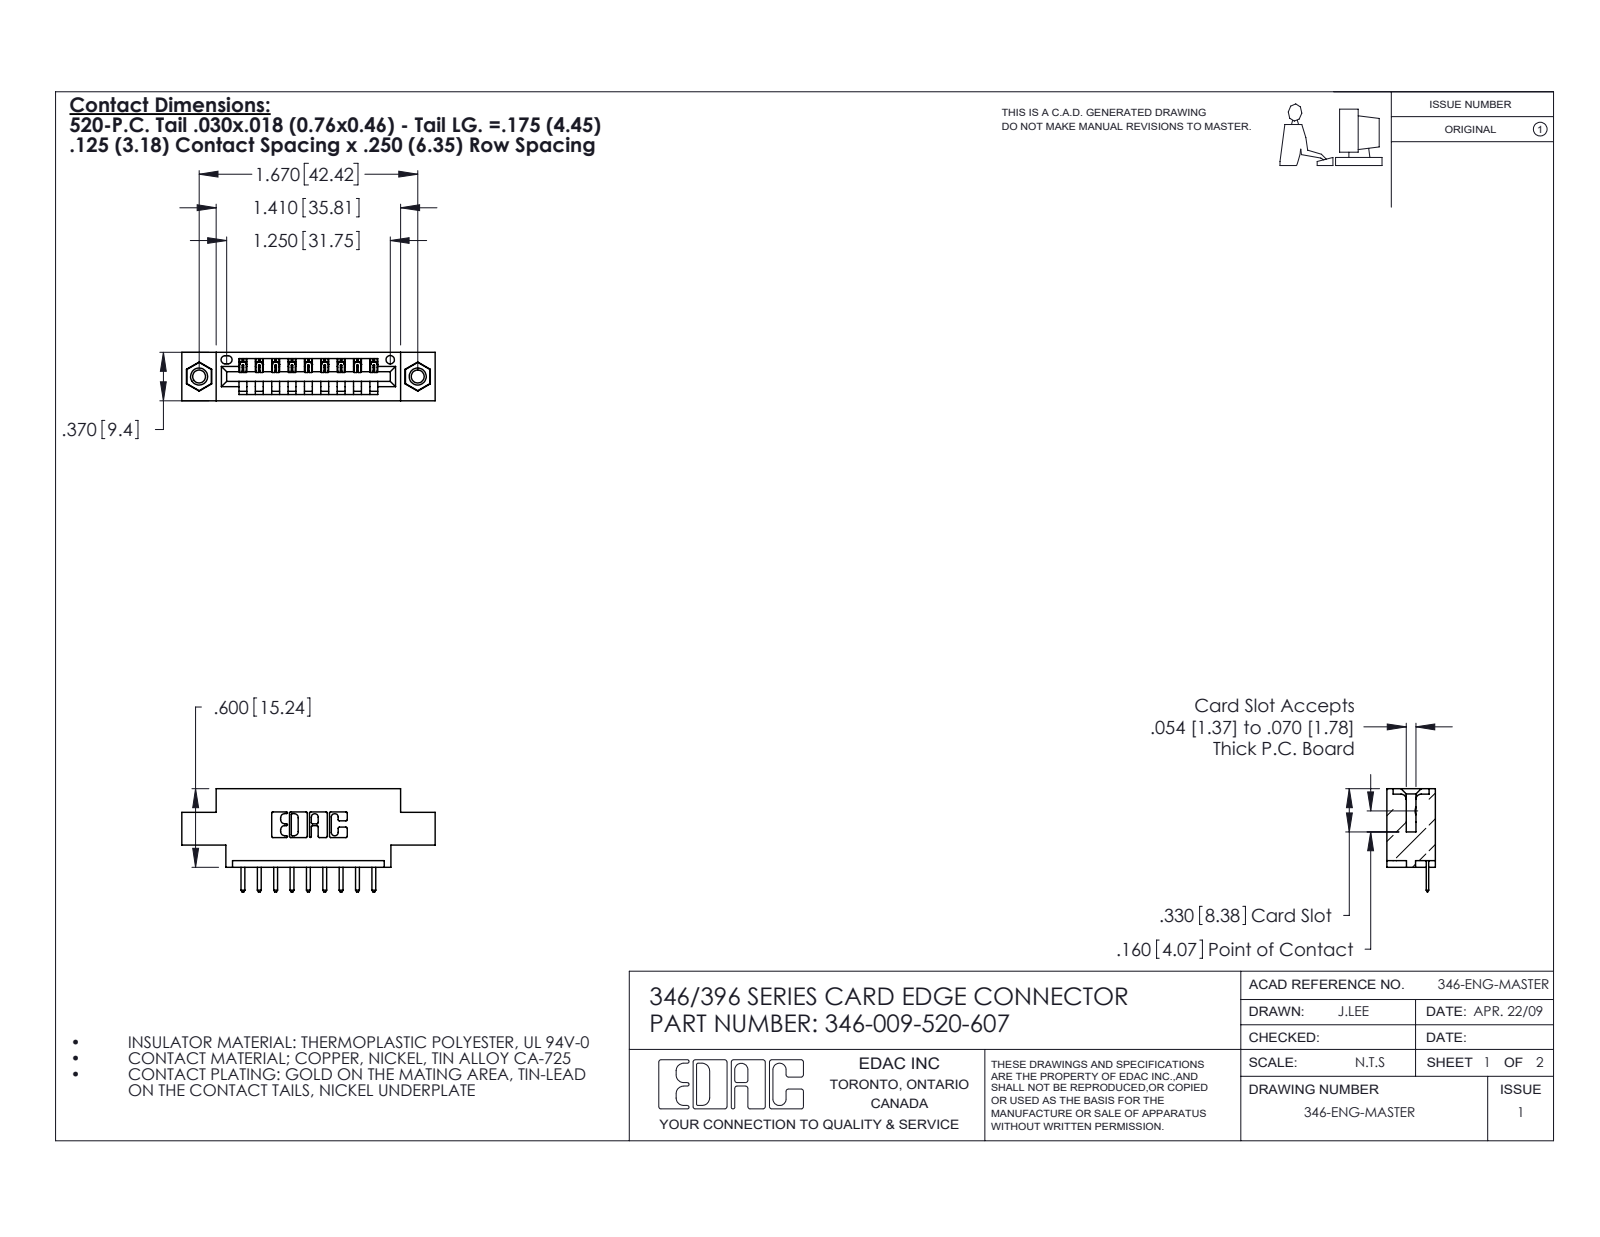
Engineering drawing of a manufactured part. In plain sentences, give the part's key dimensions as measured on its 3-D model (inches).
The part is named "346-009-520-607; 345-250-001_345-250-005-103; 345-292-001_345-293-120; 346 Part_0.170 Offset - 0.156 Dia-TI". Its 3-D file was written by "SolidWorks 2020 (CONFIG_CONTROL_DESIGN)". It is 12 solids with 744 faces: 490 planar, 238 cylindrical and 16 other. Overall it measures 1.935 by 0.788 by 0.37 inches. Its volume is 0.261 cubic inches and its surface area 7.914 square inches. Round holes: 2 of diameter 0.098, 2 of diameter 0.125, 2 of diameter 0.156, 1 of diameter 0.064. Round bosses or shafts: 2 of diameter 0.155. Partial cylindrical surfaces (rounded edges, fillets, slot ends): 22 of radius 0.01, 20 of radius 0.01, 18 of radius 0.006, 6 of radius 0.007, 6 of radius 0.031, 3 of radius 0.026, 2 of radius 0.031, 2 of radius 0.04. The main face-to-face distances are 0.25, 0.37, 0.048, 0.322, 0.222, 0.148, 0.1, 0.174, 0.072, 0.298. The hole center spacings are 0.246, 1.465, 1.67.
